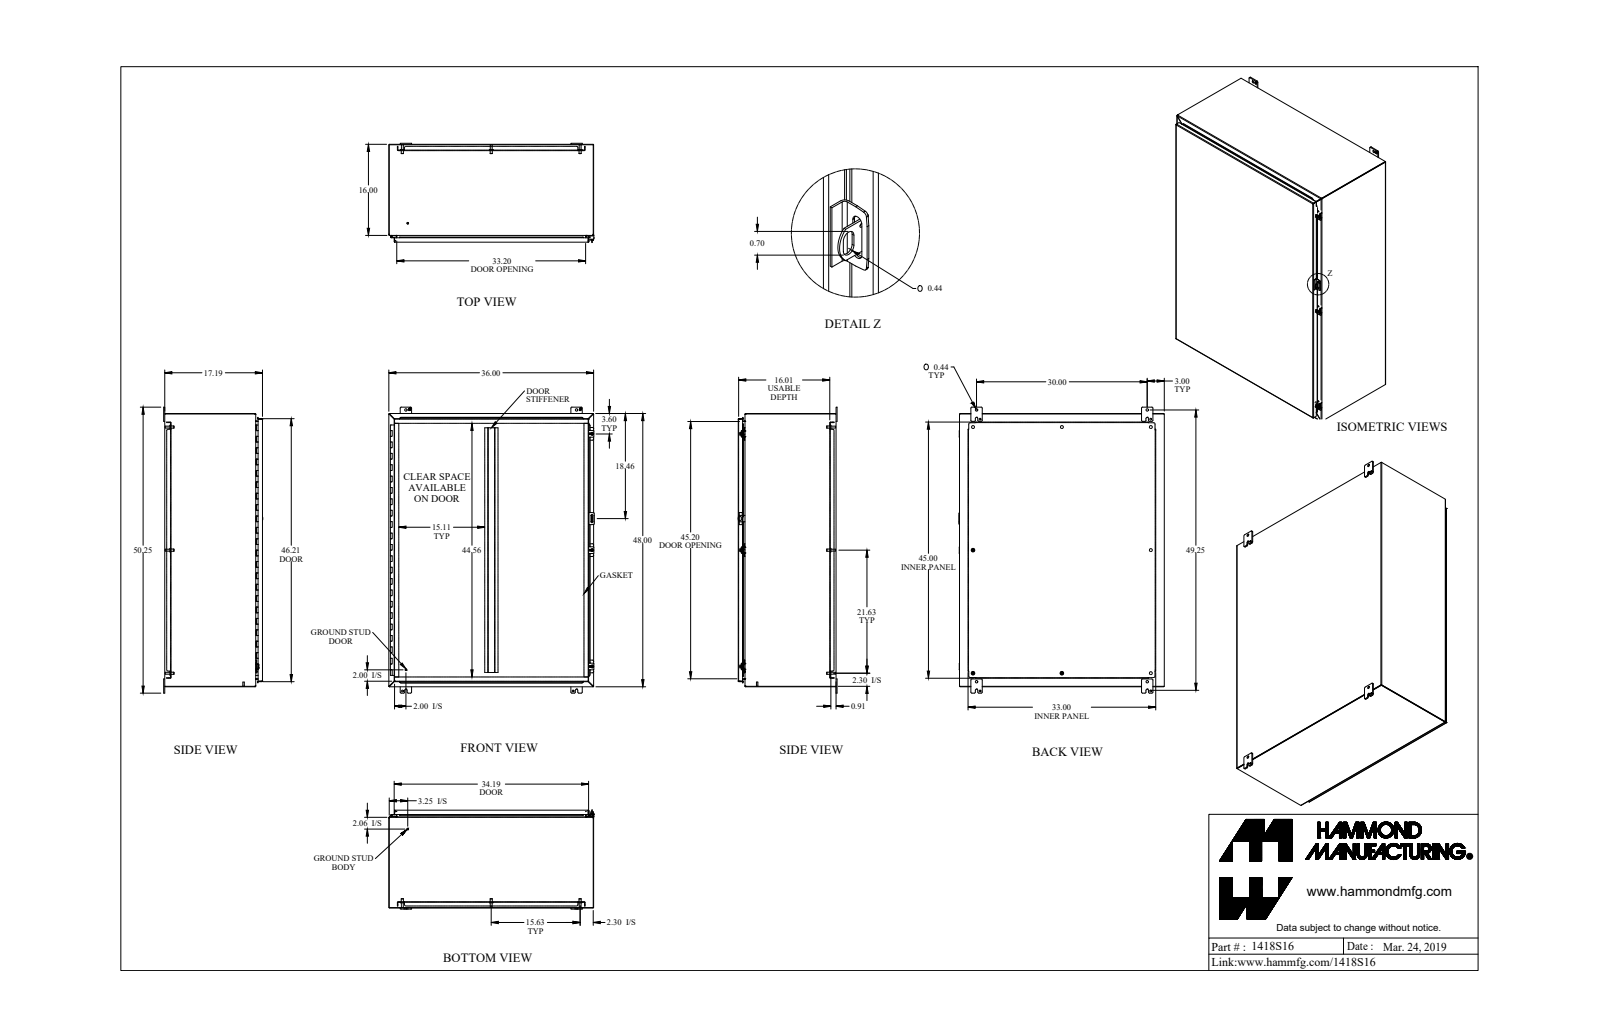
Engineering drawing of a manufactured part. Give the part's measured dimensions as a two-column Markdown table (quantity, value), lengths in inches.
| quantity | value |
| --- | --- |
| part name | 1418S16_Default |
| STEP written by | SolidWorks 2019 (CONFIG_CONTROL_DESIGN) |
| units | inches |
| bodies | 56 solids, 1736 faces (995 planar, 631 cylindrical, 110 other) |
| overall size | 50.25 × 36.125 × 17.437 |
| volume | 686.5 in³ |
| surface area | 17 935 in² |
| round holes (diameter × count) | 0.5 × 8, 0.307 × 4, 0.313 × 4, 0.437 × 4, 0.445 × 4, 0.213 × 3, 0.265 × 3, 0.375 × 3, 0.125 × 1, 0.187 × 1 |
| round bosses / shafts (diameter × count) | 0.65 × 8, 0.375 × 8, 0.33 × 8, 1 × 4, 0.5 × 3, 0.39 × 3, 0.244 × 3, 0.281 × 2 |
| partial cylindrical surfaces (radius × count) | 0.188 × 36, 0.25 × 24, 0.036 × 22, 0.108 × 22, 0.048 × 19, 0.143 × 19, 0.116 × 16, 0.04 × 8 |
| main face-to-face distances | 0.072, 17.113, 17.041, 17.185, 0.095, 0.937, 1.009, 35.928, 16.081, 16.009 |
| hole center spacings | 38.003, 15.625, 21.625, 45.986, 53.358, 1.735, 30, 31.25 |
